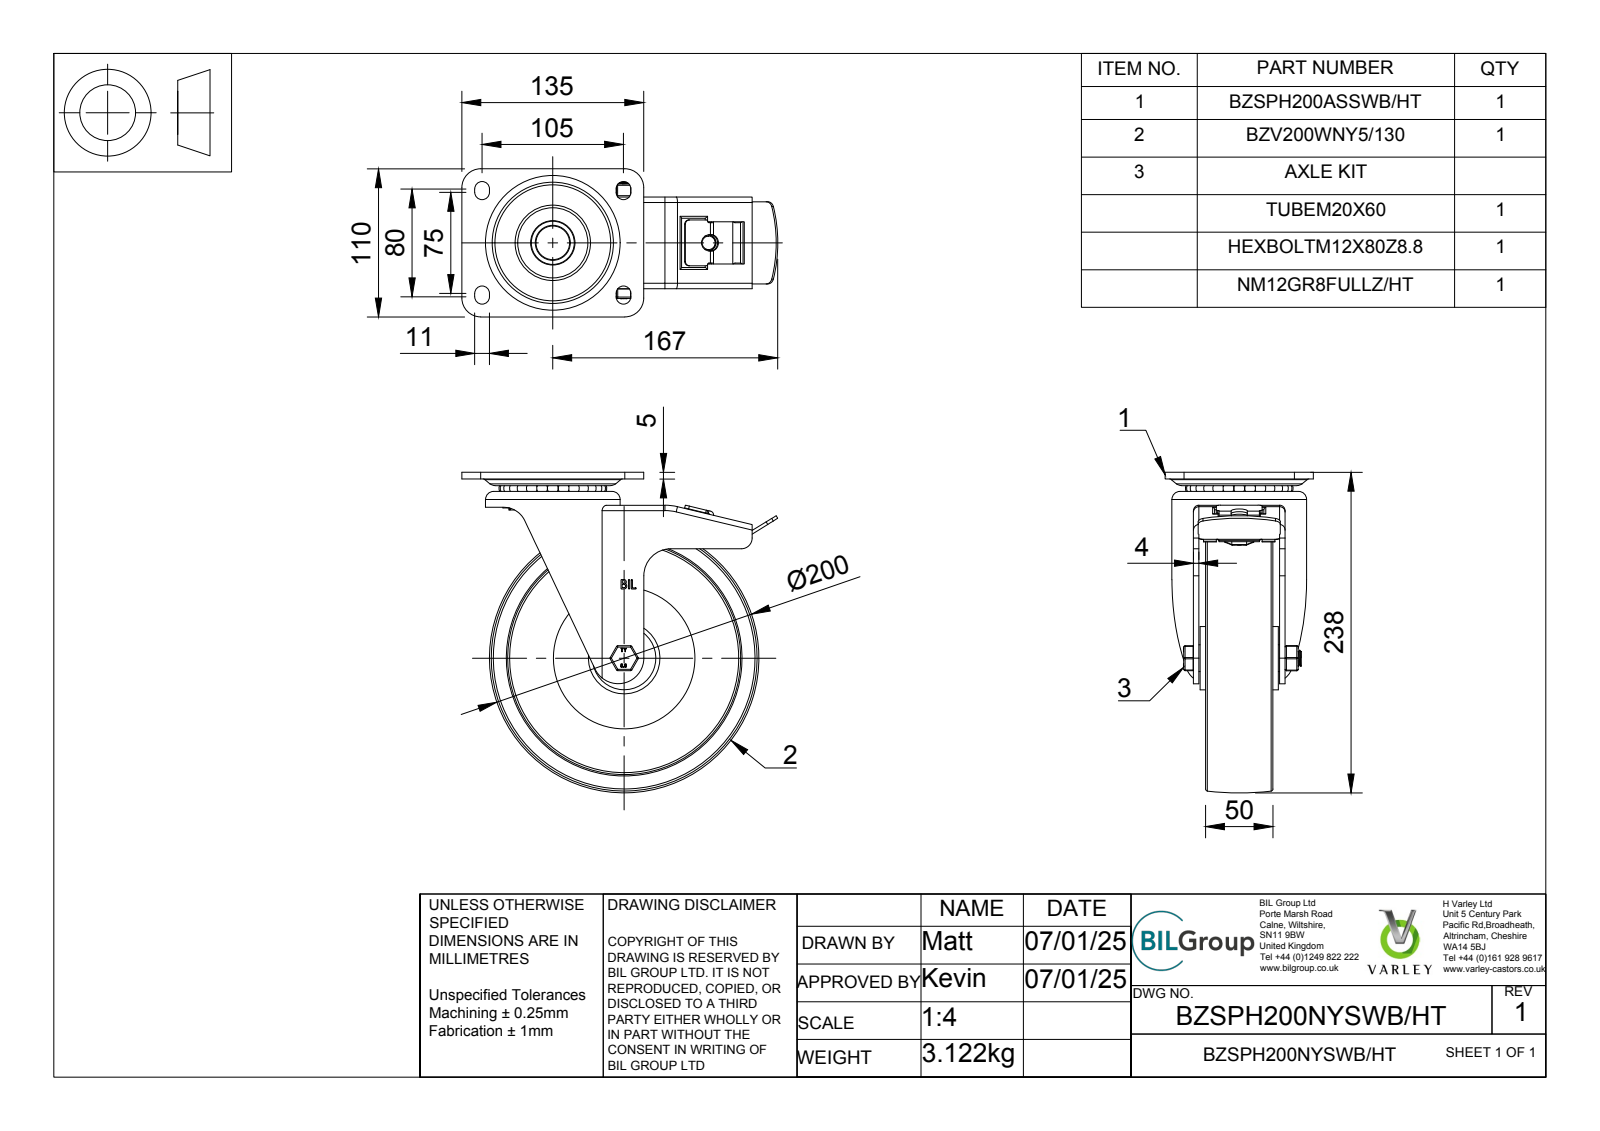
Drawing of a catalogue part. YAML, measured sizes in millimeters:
part_name: "BZSPH200NYSWB/HT v3; BZV200WNY5130 v1; FIBRE GLASS FILLED NYLON WHEEL; BZSPH200ASSWBHT - 60 v1 (+8 more)"
step_written_by: "Autodesk Translation Framework v13.20.0.188 (AP242_MANAGED_MODEL_BASED_3D_ENGINEERING_MIM_LF)"
units: millimeters
bodies: {solids: 70, faces: 682, planar: 290, cylindrical: 199, other: 193}
overall_size: [238, 234.5, 110]
volume: 1067000
surface_area: 281042
round_holes:
  - {diameter: 10, count: 1}
  - {diameter: 12, count: 1}
  - {diameter: 12.2, count: 1}
  - {diameter: 12.5, count: 1}
  - {diameter: 20.5, count: 1}
  - {diameter: 50, count: 1}
  - {diameter: 92, count: 1}
  - {diameter: 173, count: 1}
round_bosses_or_shafts:
  - {diameter: 100, count: 1}
  - {diameter: 74, count: 1}
  - {diameter: 47, count: 1}
  - {diameter: 34, count: 1}
  - {diameter: 33, count: 1}
  - {diameter: 28, count: 1}
  - {diameter: 26, count: 1}
  - {diameter: 23.75, count: 1}
partial_cylinders:
  - {radius: 1, count: 38}
  - {radius: 1.5, count: 10}
  - {radius: 2, count: 9}
  - {radius: 5.5, count: 8}
  - {radius: 3, count: 5}
  - {radius: 0.5, count: 4}
  - {radius: 2.5, count: 4}
  - {radius: 4, count: 4}
face_to_face_distances: [5, 4, 14, 59, 18, 27, 9, 23, 41, 32]
